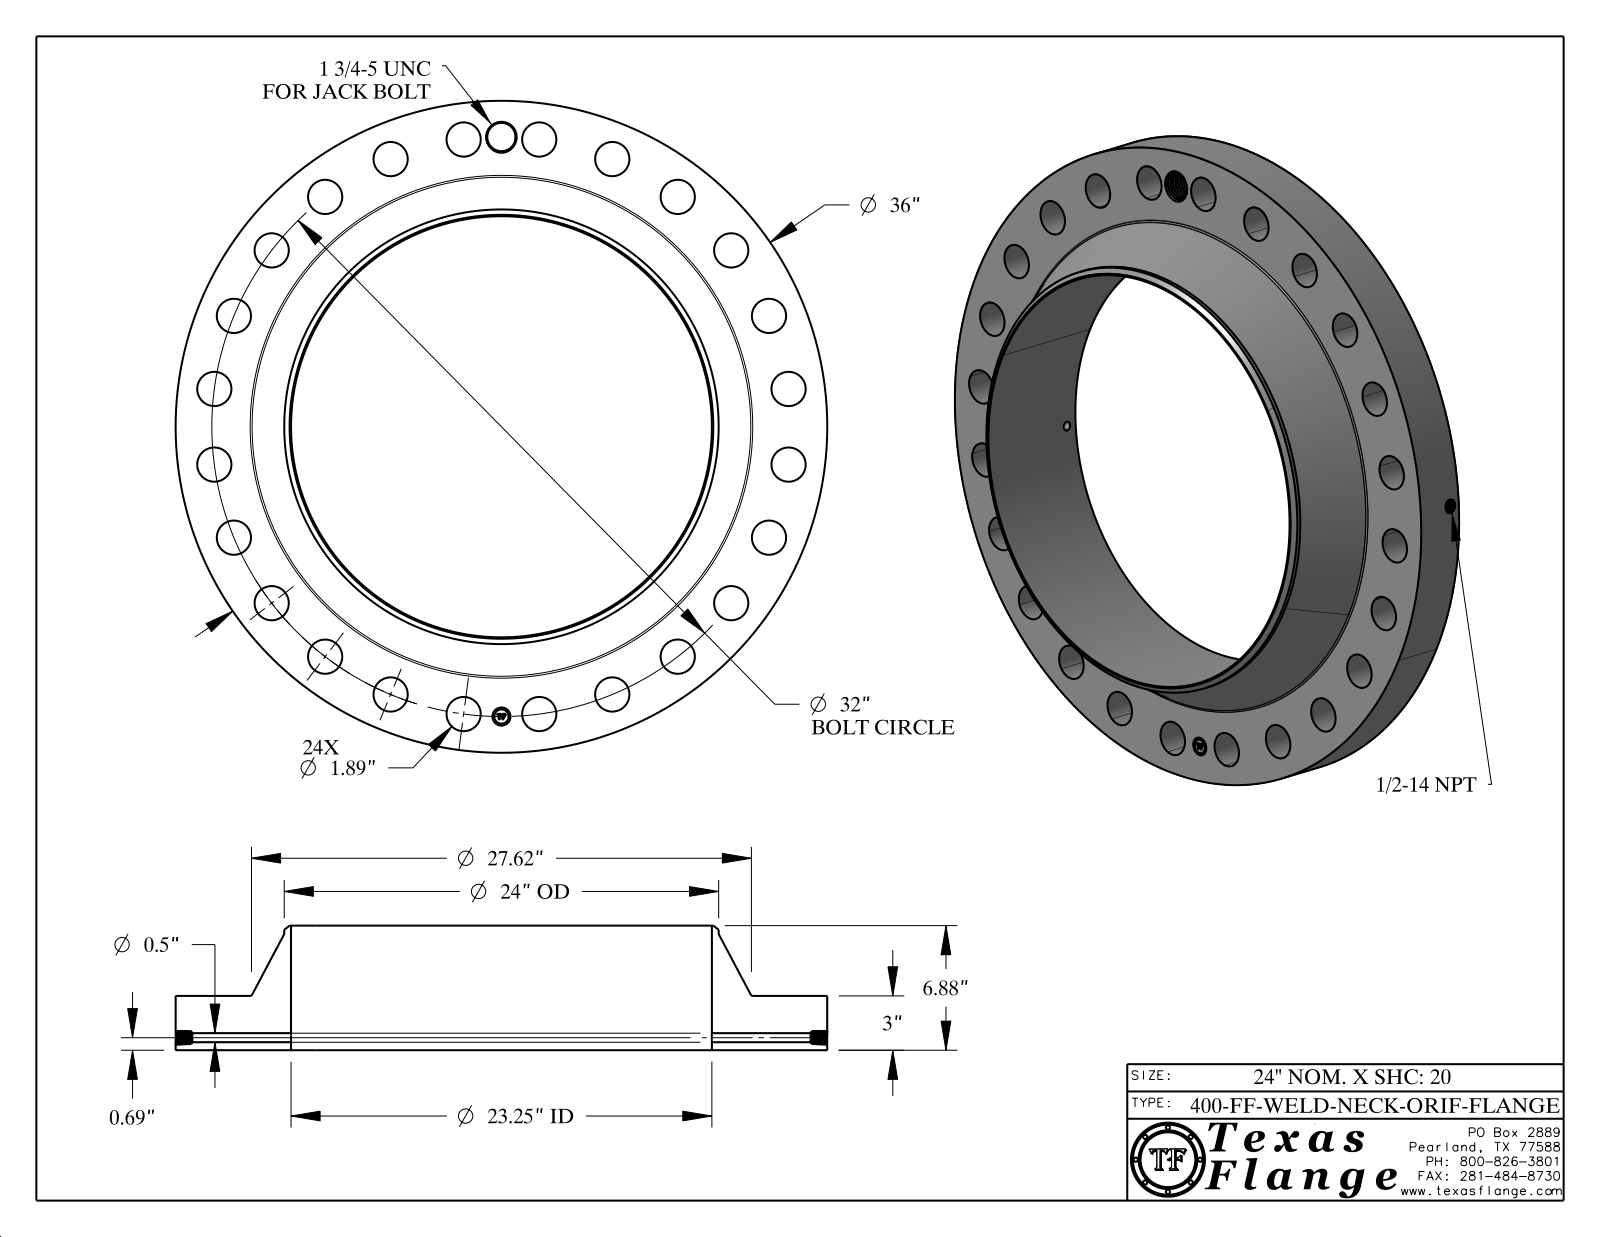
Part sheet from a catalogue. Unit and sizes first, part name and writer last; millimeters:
Units: millimetres
Overall size (bounding box): 914.4 × 914.4 × 174.8
Round holes (diameter × count): ⌀48 ×24, ⌀12.7 ×1, ⌀17.1 ×1, ⌀25.4 ×1, ⌀39.7 ×1, ⌀590.6 ×1
Round bosses / shafts (diameter × count): ⌀1.5 ×8, ⌀914.4 ×1, ⌀609.6 ×1, ⌀20 ×1
Main face-to-face distances: 76.2, 174.8, 98.6, 75.8, 0.4, 98.9, 7.6, 7.4, 1.4, 6.3
Hole centre spacings: 406.4, 703.9, 785.1, 106.1, 494.8, 805.8, 210.4, 311
Volume: 31 450 000 mm³ · Surface area: 1 646 000 mm²
Bodies: 1 solid, 798 faces (368 planar, 124 cylindrical, 306 other)
Part name (STEP PRODUCT): 400-FF-WELD-NECK
STEP written by: CATIA V5 STEP AP214 (AUTOMOTIVE_DESIGN)
